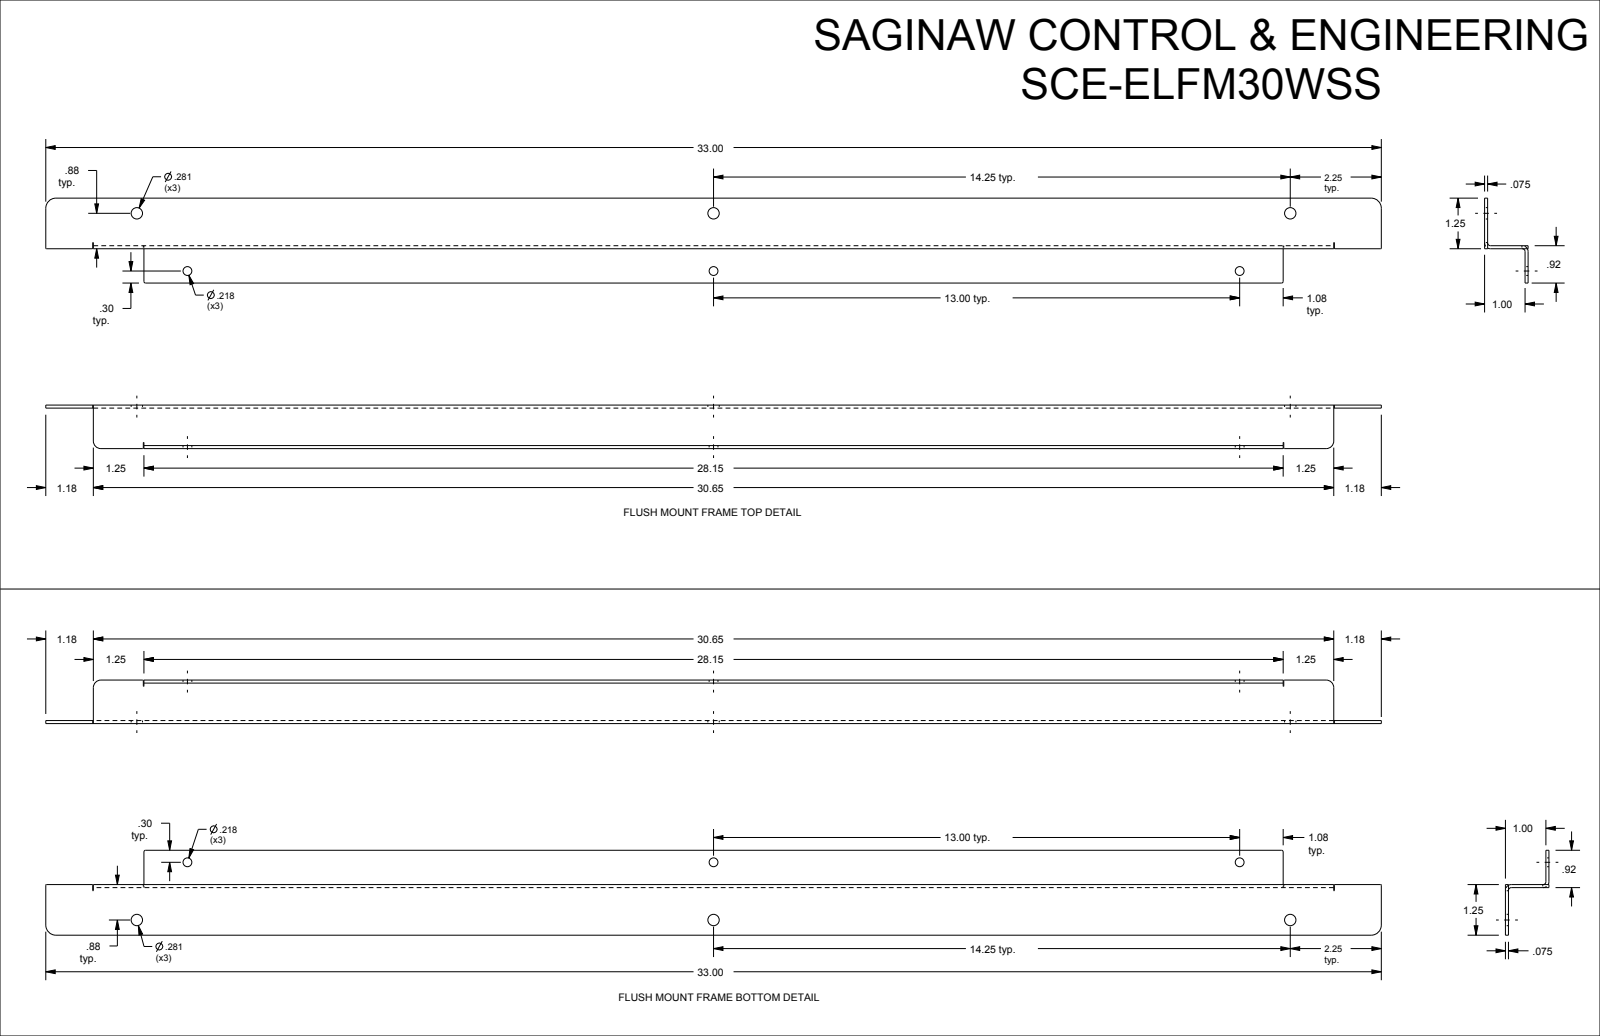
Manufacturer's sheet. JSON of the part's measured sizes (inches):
{"part_name": "SCE-ELFM30W", "step_written_by": "SolidWorks 2019 (CONFIG_CONTROL_DESIGN)", "units": "inches", "bodies": {"solids": 2, "faces": 96, "planar": 44, "cylindrical": 52, "other": 0}, "overall_size": [33, 26.35, 1.075], "volume_in3": 13.97, "surface_area_in2": 384.2, "round_holes": [[0.218, 6], [0.281, 6]], "partial_cylinders_radius": [[0.015, 10], [0.007, 6], [0.04, 4], [0.051, 4], [0.126, 4], [0.25, 4], [0.187, 2]], "face_to_face_distances": [0.075, 1, 0.075, 23.925, 1.075, 0.925, 23.85, 24, 0.922, 23.078], "hole_center_spacings": [13, 13.078, 14.25, 26.202, 27.287, 29.299, 36.428, 22.75]}
